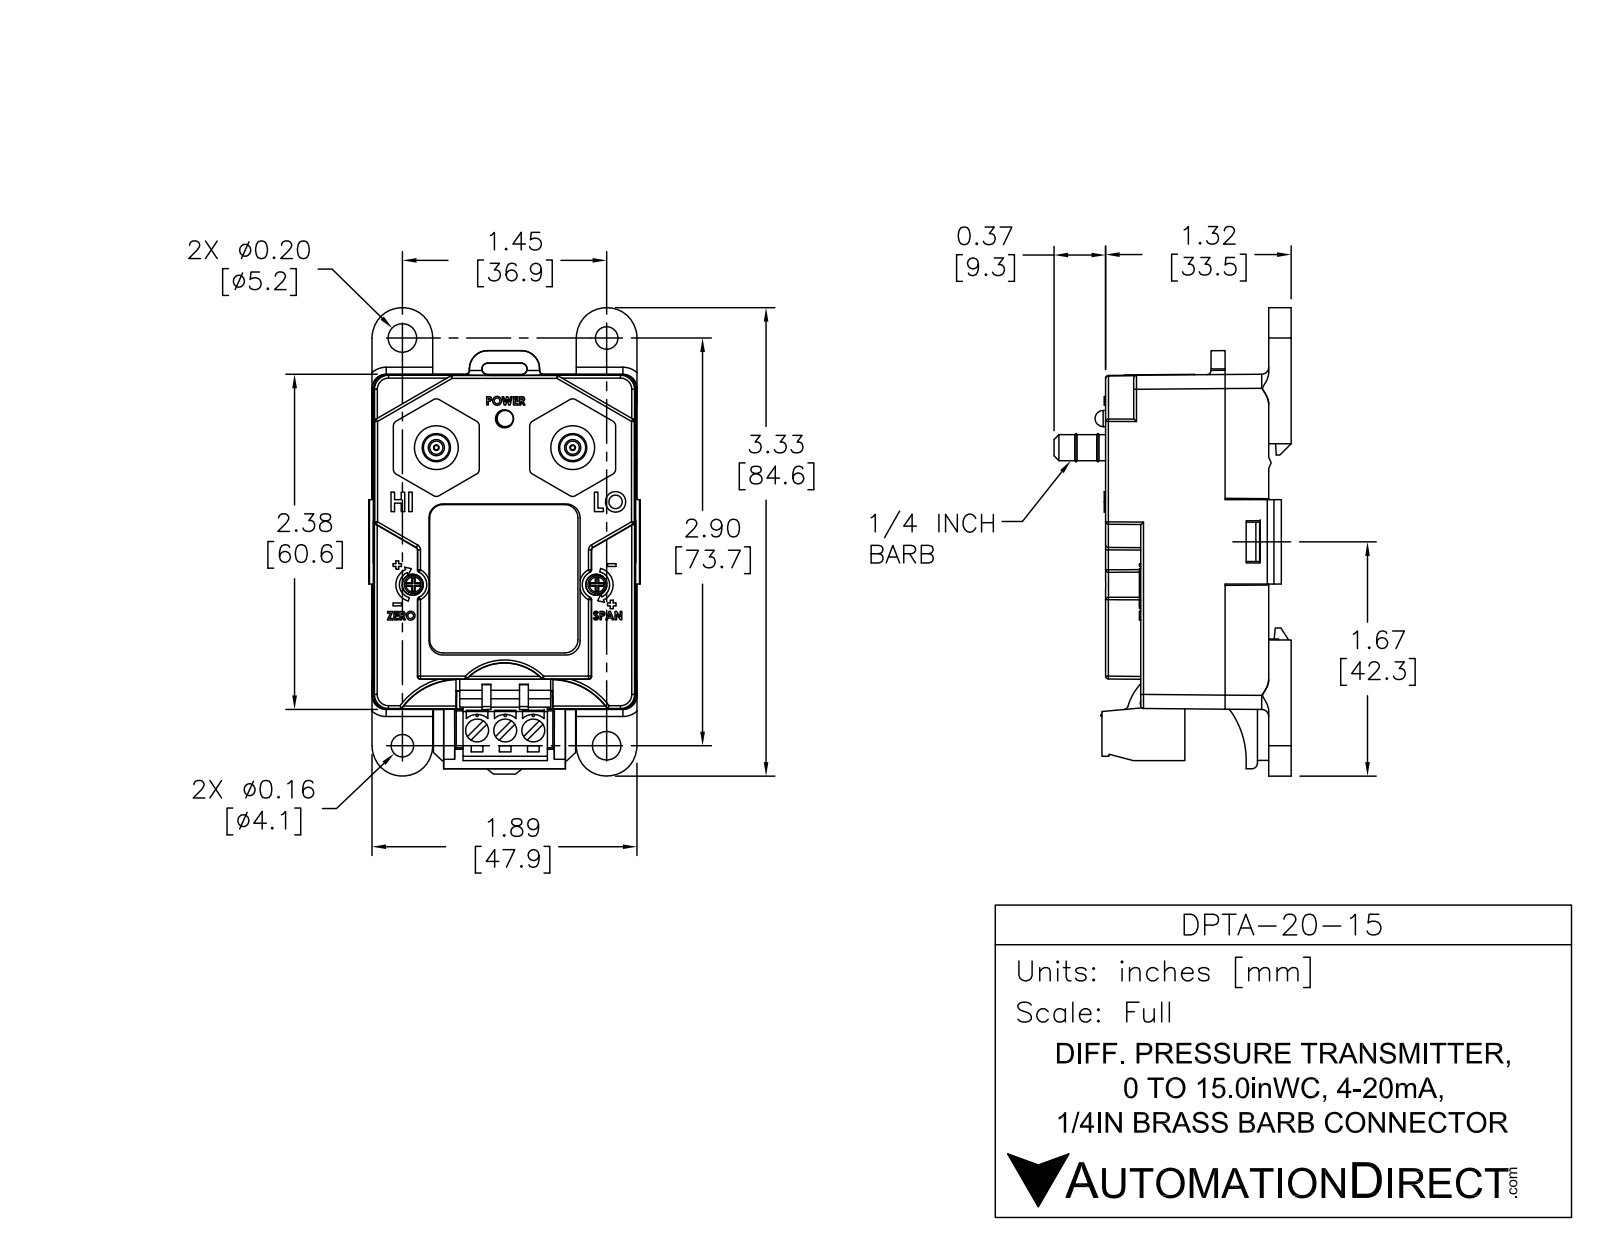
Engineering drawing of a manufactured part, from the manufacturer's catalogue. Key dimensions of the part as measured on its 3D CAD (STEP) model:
Part name (STEP PRODUCT): DPTA-20-15
STEP written by: SolidWorks 2011 (AUTOMOTIVE_DESIGN)
Units: millimetres
Bodies: 11 solids, 448 faces (354 planar, 85 cylindrical, 9 other)
Overall size (bounding box): 85.01 × 49.76 × 43.1
Volume: 29 684 mm³ · Surface area: 34 743 mm²
Round holes (diameter × count): ⌀4 ×7, ⌀2.5 ×2, ⌀5.12 ×2, ⌀3.1 ×1
Round bosses / shafts (diameter × count): ⌀5 ×3, ⌀3.5 ×3, ⌀3.5 ×3, ⌀8 ×2, ⌀4.75 ×2, ⌀3 ×1
Partial cylindrical surfaces — rounded edges, fillets, slot ends (radius × count): R3 ×12, R2 ×4, R5.5 ×4, R0.99 ×2, R1.06 ×2, R1.12 ×2, R2.38 ×2, R3.25 ×2
Main face-to-face distances: 1, 1.9, 4, 29.1, 0.5, 46.9, 5.9, 5, 33.1, 27.2
Hole centre spacings: 13.55, 20.73, 23.37, 24.92, 29.43, 34.46, 36.67, 38.22
